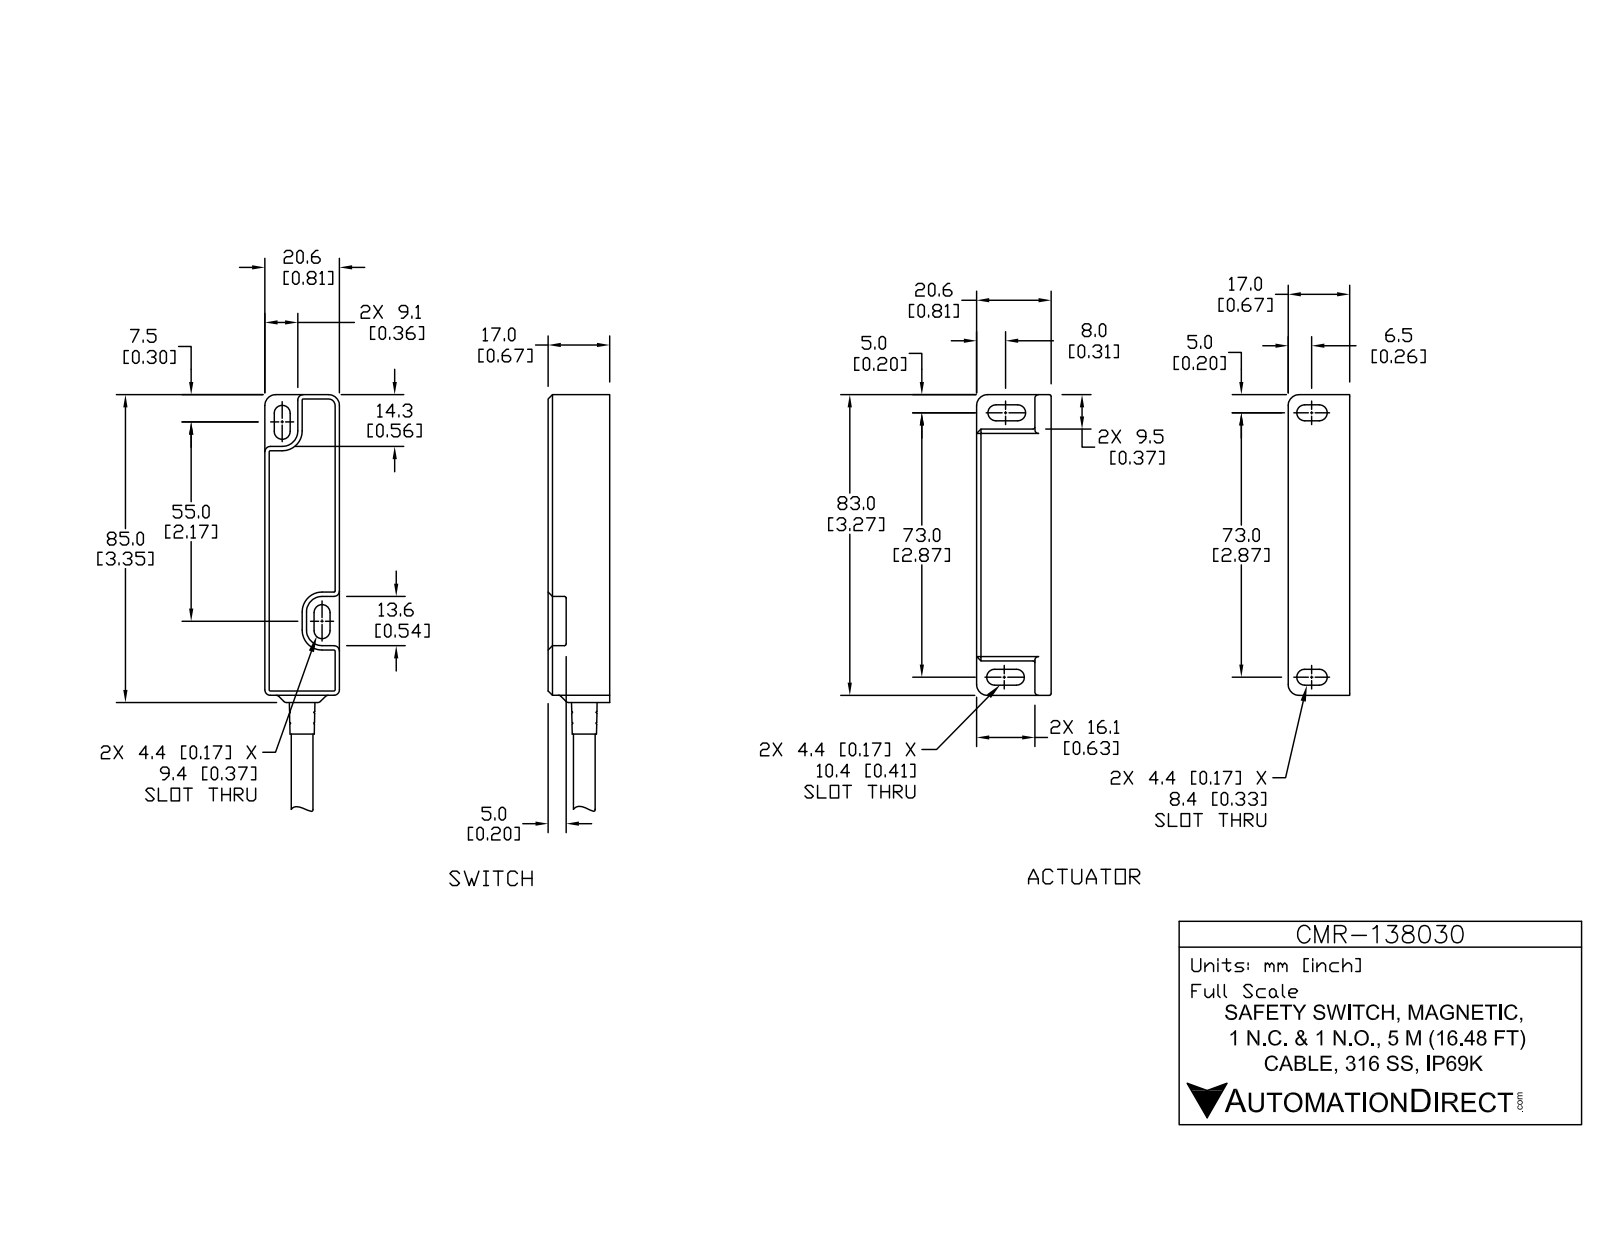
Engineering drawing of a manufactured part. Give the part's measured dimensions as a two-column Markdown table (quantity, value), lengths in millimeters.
| quantity | value |
| --- | --- |
| part name | CMR-138030_1; CMR-138030_2; CMR-138030 |
| STEP written by | SolidWorks 2017 (AUTOMOTIVE_DESIGN) |
| units | millimeters |
| bodies | 10 solids, 652 faces (215 planar, 239 cylindrical, 198 other) |
| overall size | 243.6 × 42.2 × 17 |
| volume | 30 910 mm³ |
| surface area | 31 630 mm² |
| round holes (diameter × count) | 5 × 4, 4.2 × 1, 5.9 × 1, 7.2 × 1 |
| round bosses / shafts (diameter × count) | 4.9 × 4, 2 × 4, 8.6 × 1, 7.6 × 1, 7.1 × 1, 6 × 1 |
| partial cylindrical surfaces (radius × count) | 0.5 × 94, 0.3 × 15, 2.2 × 12, 1 × 10, 1.5 × 6, 3 × 6, 0.2 × 4, 0.7 × 3 |
| main face-to-face distances | 1.8, 21.6, 18.8, 17, 20.6, 40.4, 19.8, 16.8, 14.8, 2 |
| hole center spacings | 1.3, 27.1, 27.4, 28.4, 49, 63.1, 64.3, 65.6 |
